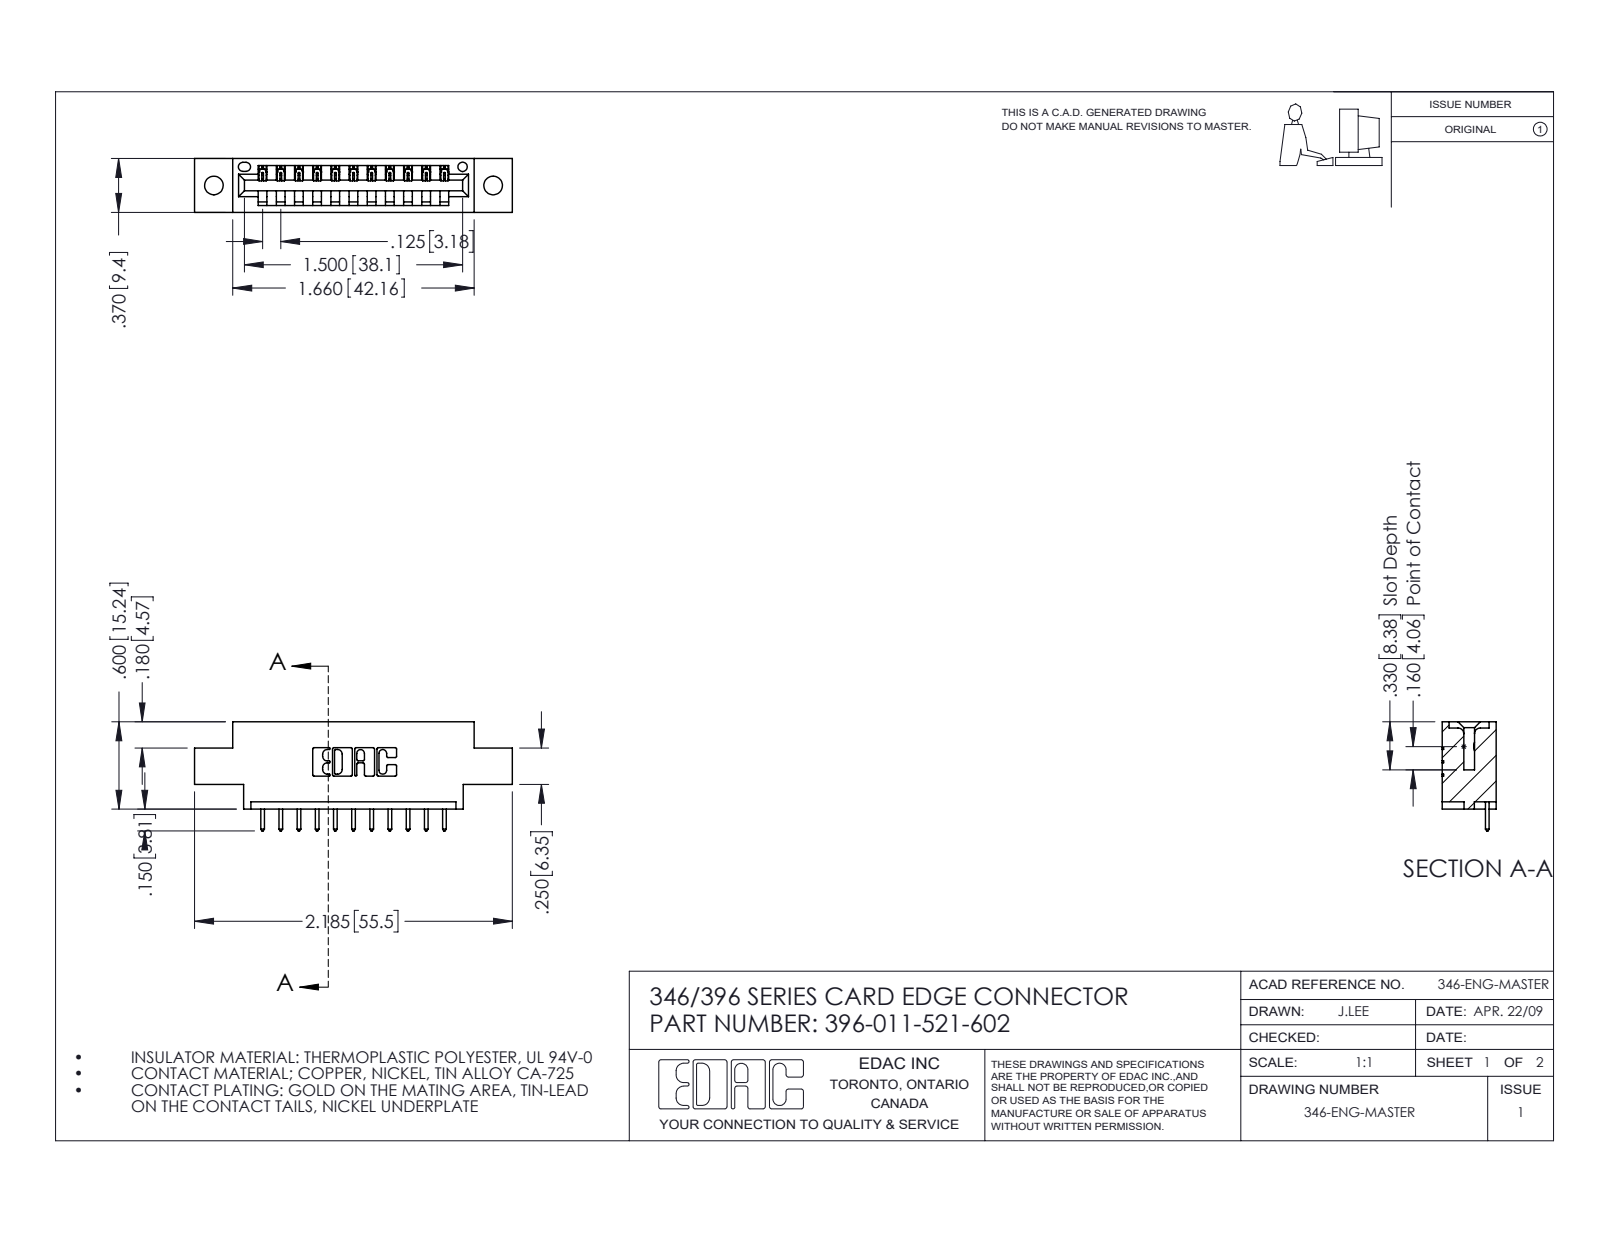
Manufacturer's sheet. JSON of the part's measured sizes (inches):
{"part_name": "345-292-001_345-293-121; 346 Part_0.170 Offset - 0.128 Dia; 396-011-521-602", "step_written_by": "SolidWorks 2016 (CONFIG_CONTROL_DESIGN)", "units": "inches", "bodies": {"solids": 12, "faces": 764, "planar": 520, "cylindrical": 244, "other": 0}, "overall_size": [2.185, 0.75, 0.37], "volume_in3": 0.298, "surface_area_in2": 8.564, "round_holes": [[0.128, 2], [0.064, 1]], "partial_cylinders_radius": [[0.006, 22], [0.01, 22], [0.01, 22], [0.007, 6], [0.031, 6], [0.026, 3], [0.031, 2], [0.04, 2]], "face_to_face_distances": [0.25, 0.37, 0.048, 0.322, 0.148, 0.222, 0.1, 0.174, 0.072, 0.298], "hole_center_spacings": [0.246, 1.715, 1.92]}
